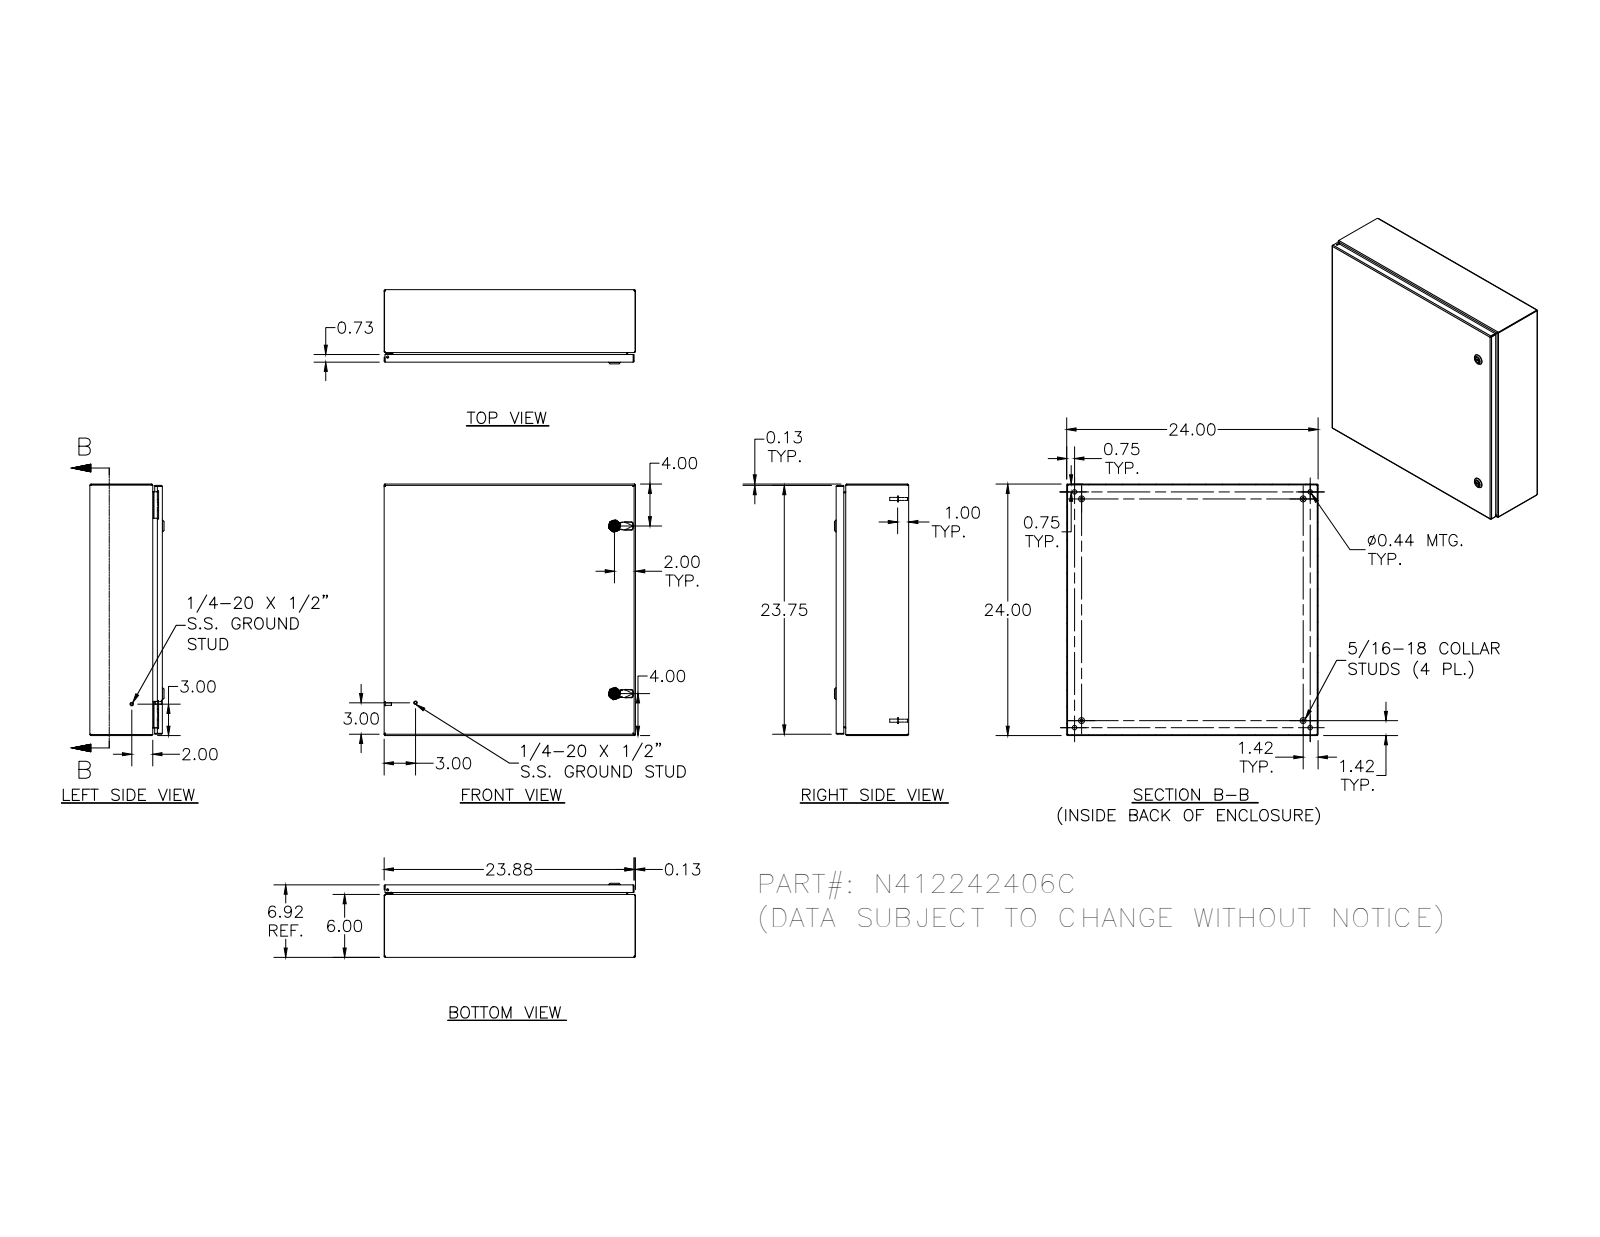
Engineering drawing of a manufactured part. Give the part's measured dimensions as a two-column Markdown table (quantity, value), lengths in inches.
| quantity | value |
| --- | --- |
| part name | N412242406C |
| STEP written by | SolidWorks 2018 (AUTOMOTIVE_DESIGN) |
| units | inches |
| bodies | 40 solids, 1812 faces (704 planar, 676 cylindrical, 432 other) |
| overall size | 24 × 24 × 7.075 |
| volume | 142.8 in³ |
| surface area | 3 875 in² |
| round holes (diameter × count) | 0.188 × 5, 0.093 × 4, 0.152 × 4, 0.167 × 4, 0.172 × 4, 0.437 × 4, 0.156 × 2, 0.197 × 2, 0.315 × 2, 0.394 × 2, 0.402 × 2, 0.634 × 2 |
| round bosses / shafts (diameter × count) | 0.25 × 10, 0.563 × 4, 0.36 × 4, 0.32 × 4, 0.3 × 4, 0.256 × 4, 0.164 × 4, 0.131 × 4 |
| partial cylindrical surfaces (radius × count) | 0.012 × 54, 0.031 × 30, 0.05 × 26, 0.02 × 23, 0.105 × 20, 0.016 × 18, 0.125 × 16, 0.032 × 8 |
| main face-to-face distances | 0.074, 6.843, 6.769, 6.917, 0.074, 23.926, 23.926, 24, 23.852, 0.917 |
| hole center spacings | 20, 0.66, 0.656, 1.307, 1.965, 19.34, 20.66, 1.619 |
